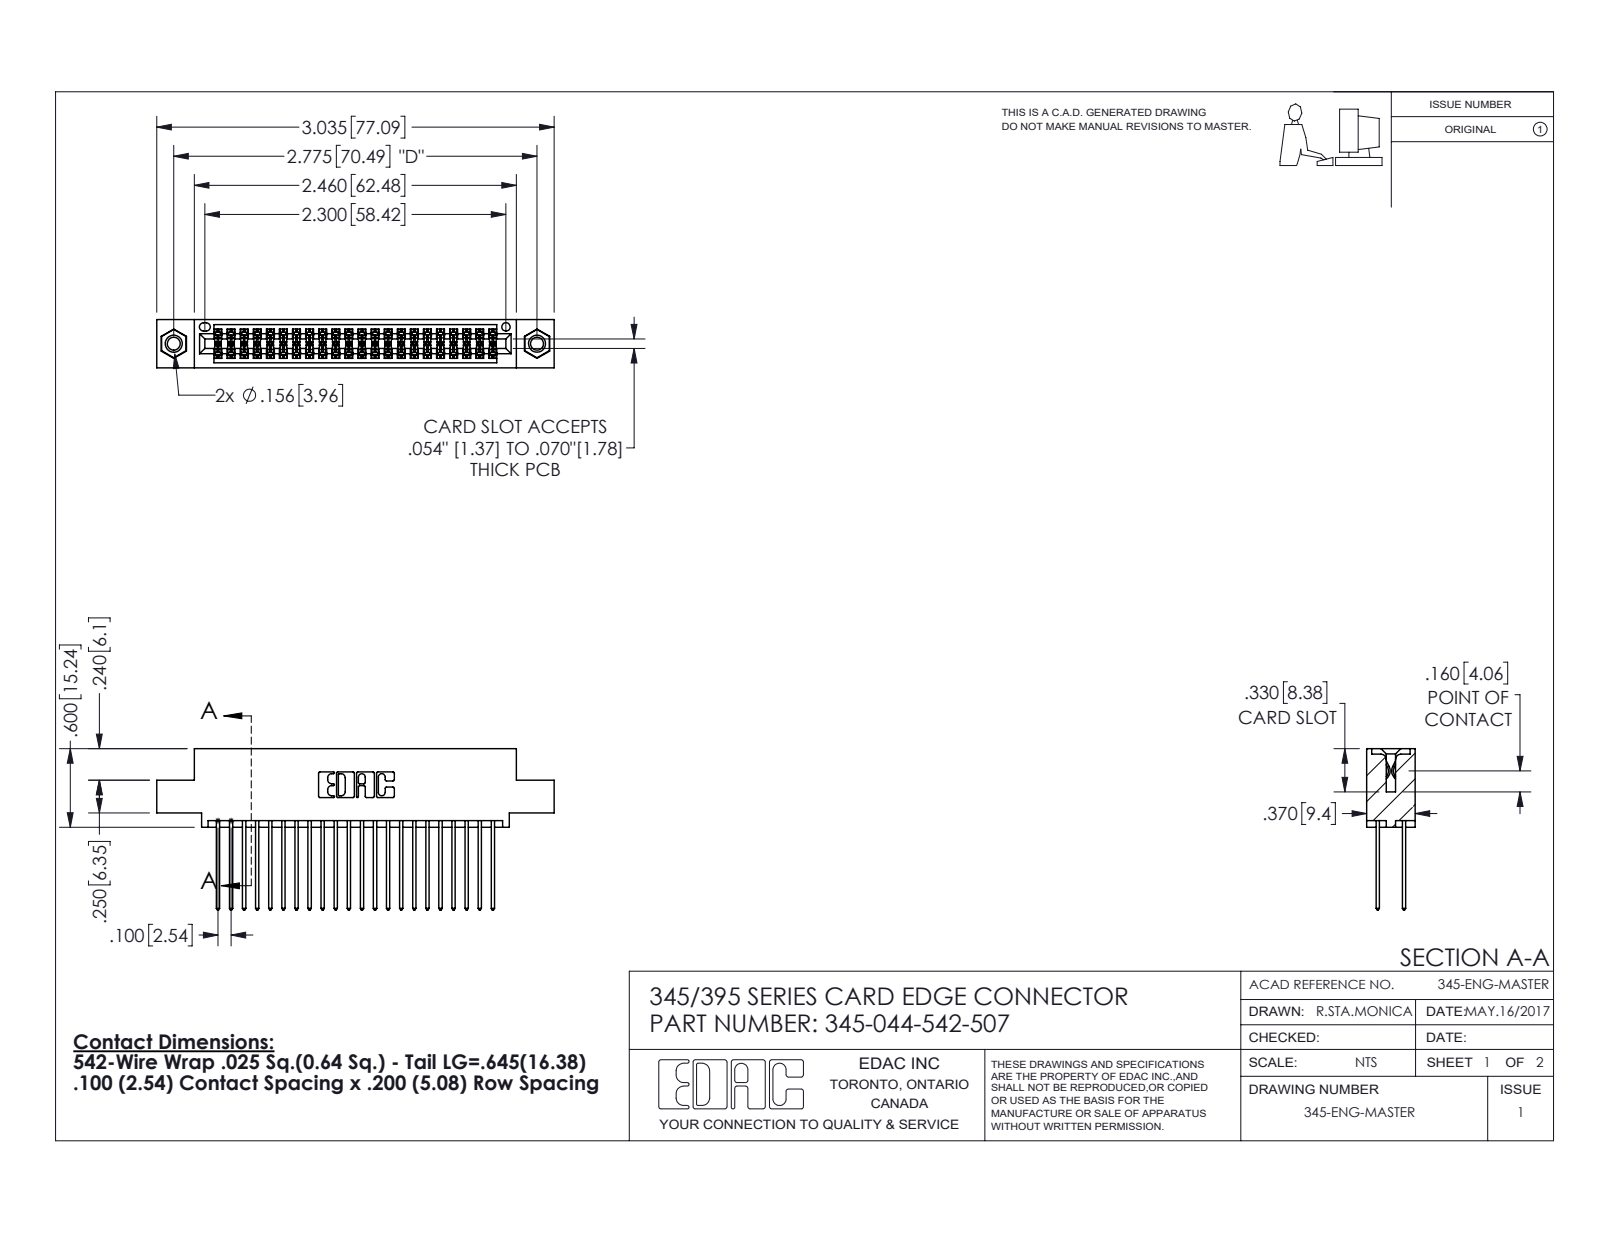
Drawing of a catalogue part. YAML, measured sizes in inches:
part_name: "345-250-001_345-250-005-103; 345-044-542-507; 345 Part_0.110 Offset - 0.156 Dia-TI; 345-292-001_345-293-142"
step_written_by: "SolidWorks 2016 (CONFIG_CONTROL_DESIGN)"
units: inches
bodies: {solids: 47, faces: 2390, planar: 1568, cylindrical: 806, other: 16}
overall_size: [3.035, 1.232, 0.37]
volume: 0.453
surface_area: 18.08
round_holes:
  - {diameter: 0.098, count: 2}
  - {diameter: 0.125, count: 2}
  - {diameter: 0.156, count: 2}
  - {diameter: 0.064, count: 1}
round_bosses_or_shafts:
  - {diameter: 0.155, count: 2}
partial_cylinders:
  - {radius: 0.006, count: 66}
  - {radius: 0.01, count: 44}
  - {radius: 0.01, count: 22}
  - {radius: 0.007, count: 6}
  - {radius: 0.031, count: 6}
  - {radius: 0.026, count: 3}
  - {radius: 0.014, count: 2}
  - {radius: 0.019, count: 2}
face_to_face_distances: [0.072, 0.298, 0.2, 0.098, 0.272, 0.025, 0.37, 0.225, 0.175, 0.149]
hole_center_spacings: [0.27, 2.541, 2.775]
